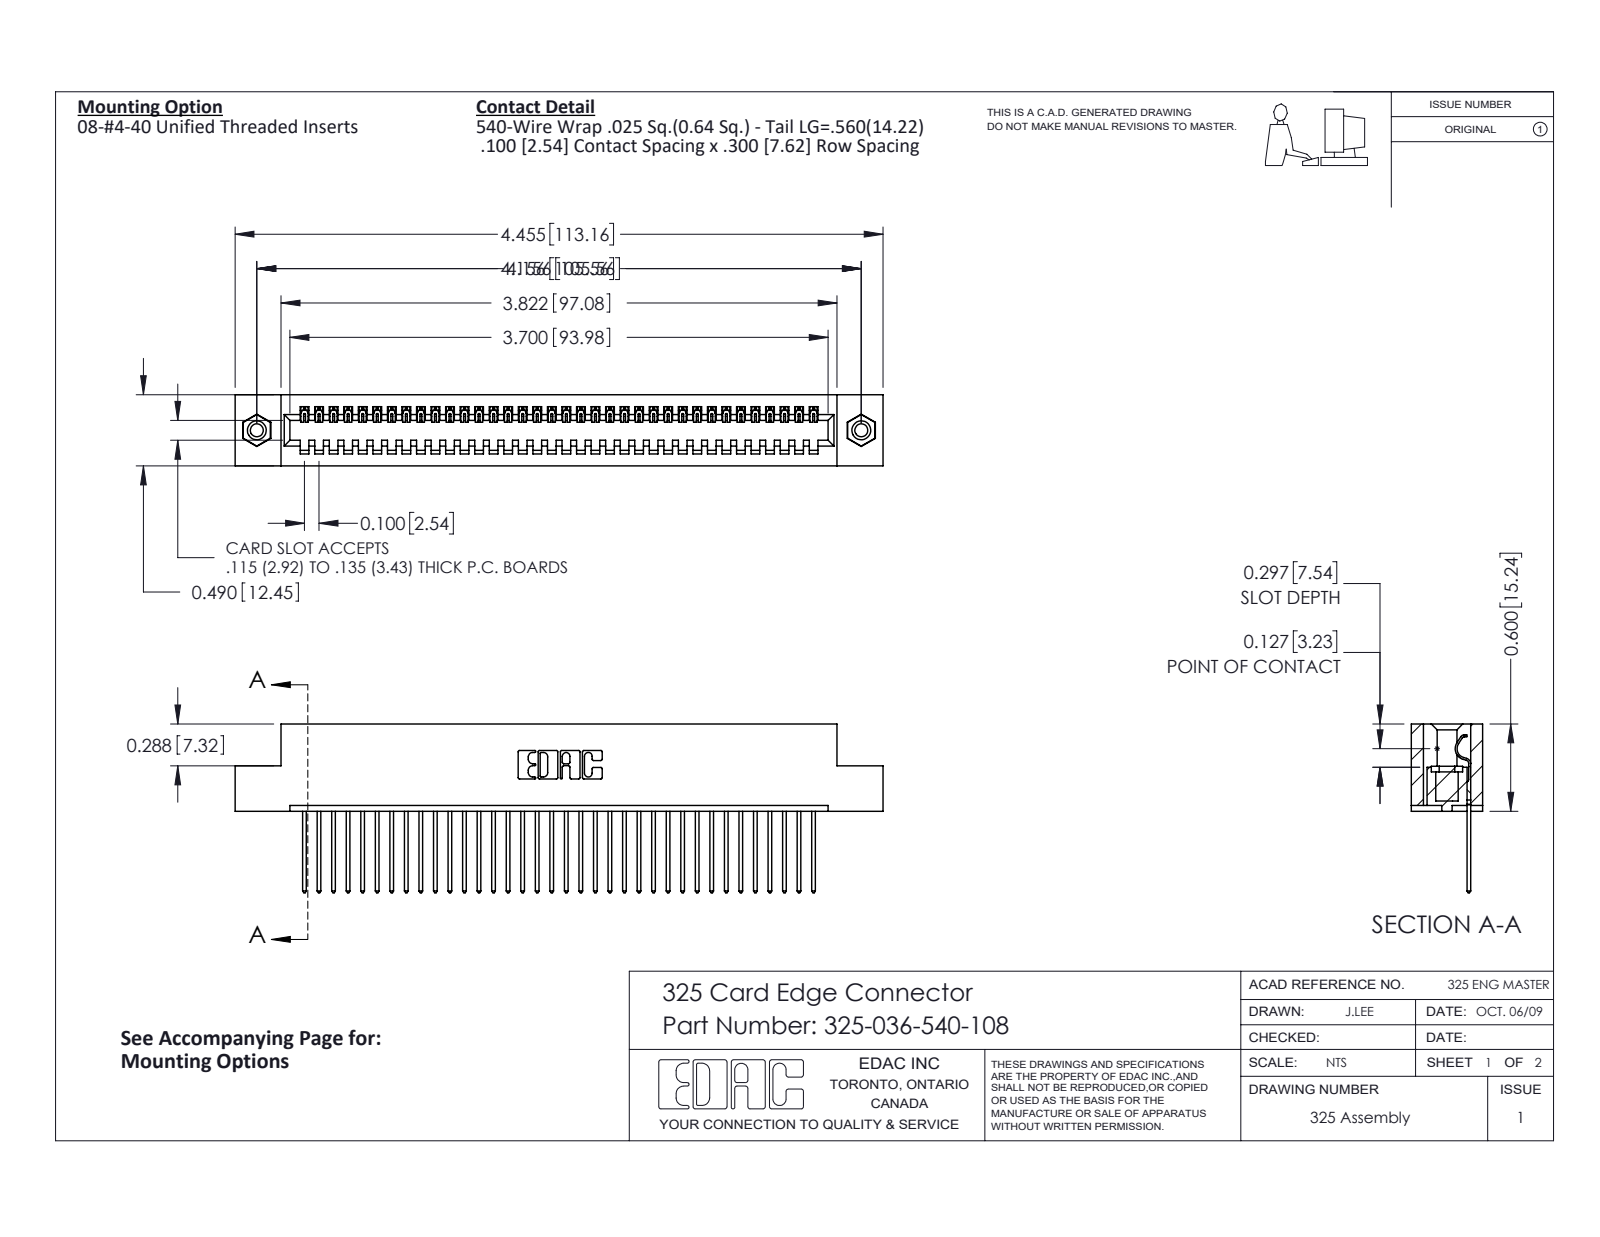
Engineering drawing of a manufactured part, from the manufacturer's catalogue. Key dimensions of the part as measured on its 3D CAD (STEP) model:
Part name (STEP PRODUCT): 325 Part_TI; 325-292-001_325-293-140; 345-250-001_345-250-003-102; 325-036-540-108
STEP written by: SolidWorks 2016 (CONFIG_CONTROL_DESIGN)
Units: inches
Bodies: 39 solids, 2262 faces (1614 planar, 632 cylindrical, 16 other)
Overall size (bounding box): 4.455 × 1.16 × 0.49
Volume: 0.876 in³ · Surface area: 24.74 in²
Round holes (diameter × count): ⌀0.089 ×2, ⌀0.125 ×2, ⌀0.16 ×2
Round bosses / shafts (diameter × count): ⌀0.155 ×2
Partial cylindrical surfaces — rounded edges, fillets, slot ends (radius × count): R0.006 ×72, R0.01 ×72, R0.01 ×22, R0.007 ×6, R0.031 ×6, R0.026 ×3, R0.014 ×1, R0.022 ×1
Main face-to-face distances: 0.083, 0.407, 0.49, 0.3, 0.107, 0.383, 0.025, 0.325, 0.56, 0.04
Hole centre spacings: 4.156
